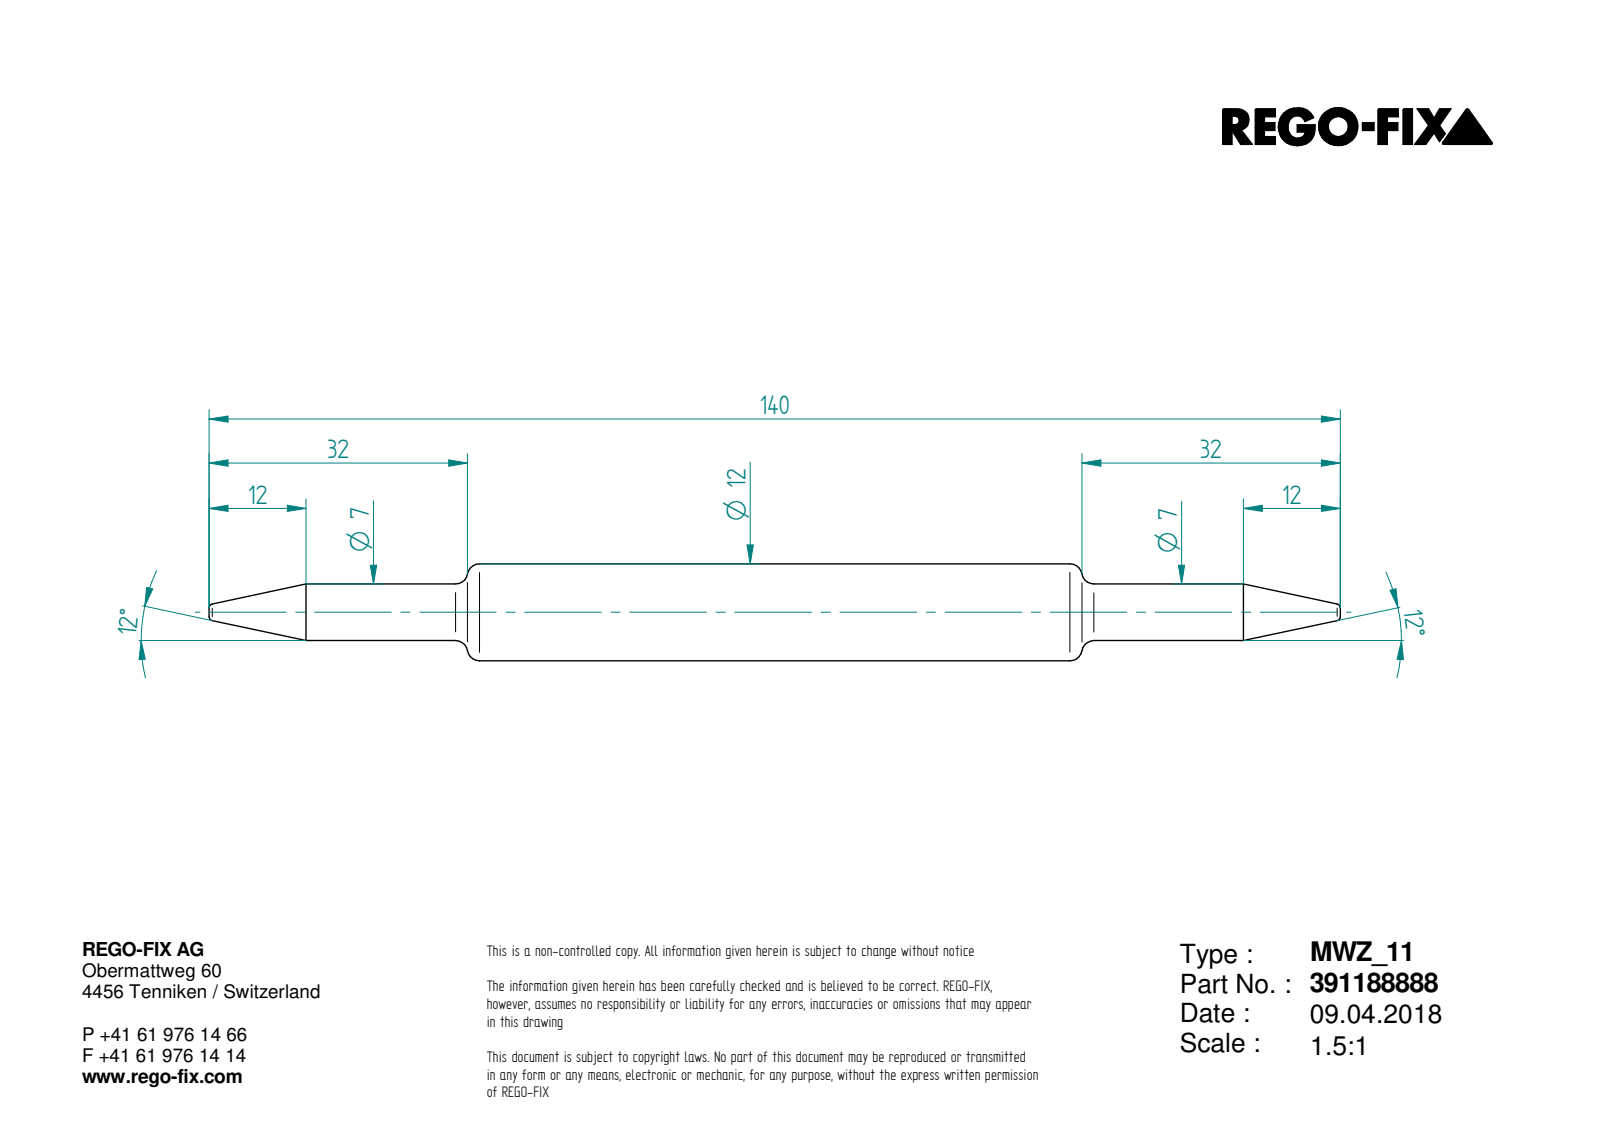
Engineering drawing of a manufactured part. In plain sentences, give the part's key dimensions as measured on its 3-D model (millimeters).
The part is named "0020187". Its 3-D file was written by "ST-DEVELOPER v16.7 (AUTOMOTIVE_DESIGN)". It is 1 solid with 138 faces: 70 planar, 19 cylindrical and 49 other. Overall it measures 140 by 12 by 12 millimeters. Its volume is 10 539 cubic millimeters and its surface area 4 176 square millimeters. Round bosses or shafts: 1 of diameter 12, 1 of diameter 7. Partial cylindrical surfaces (rounded edges, fillets, slot ends): 1 of radius 5.95. The main face-to-face distances are 140, 1.94, 67.87, 72.13, 67.1, 0.77, 72.9, 8.31, 86.19, 19.09.
